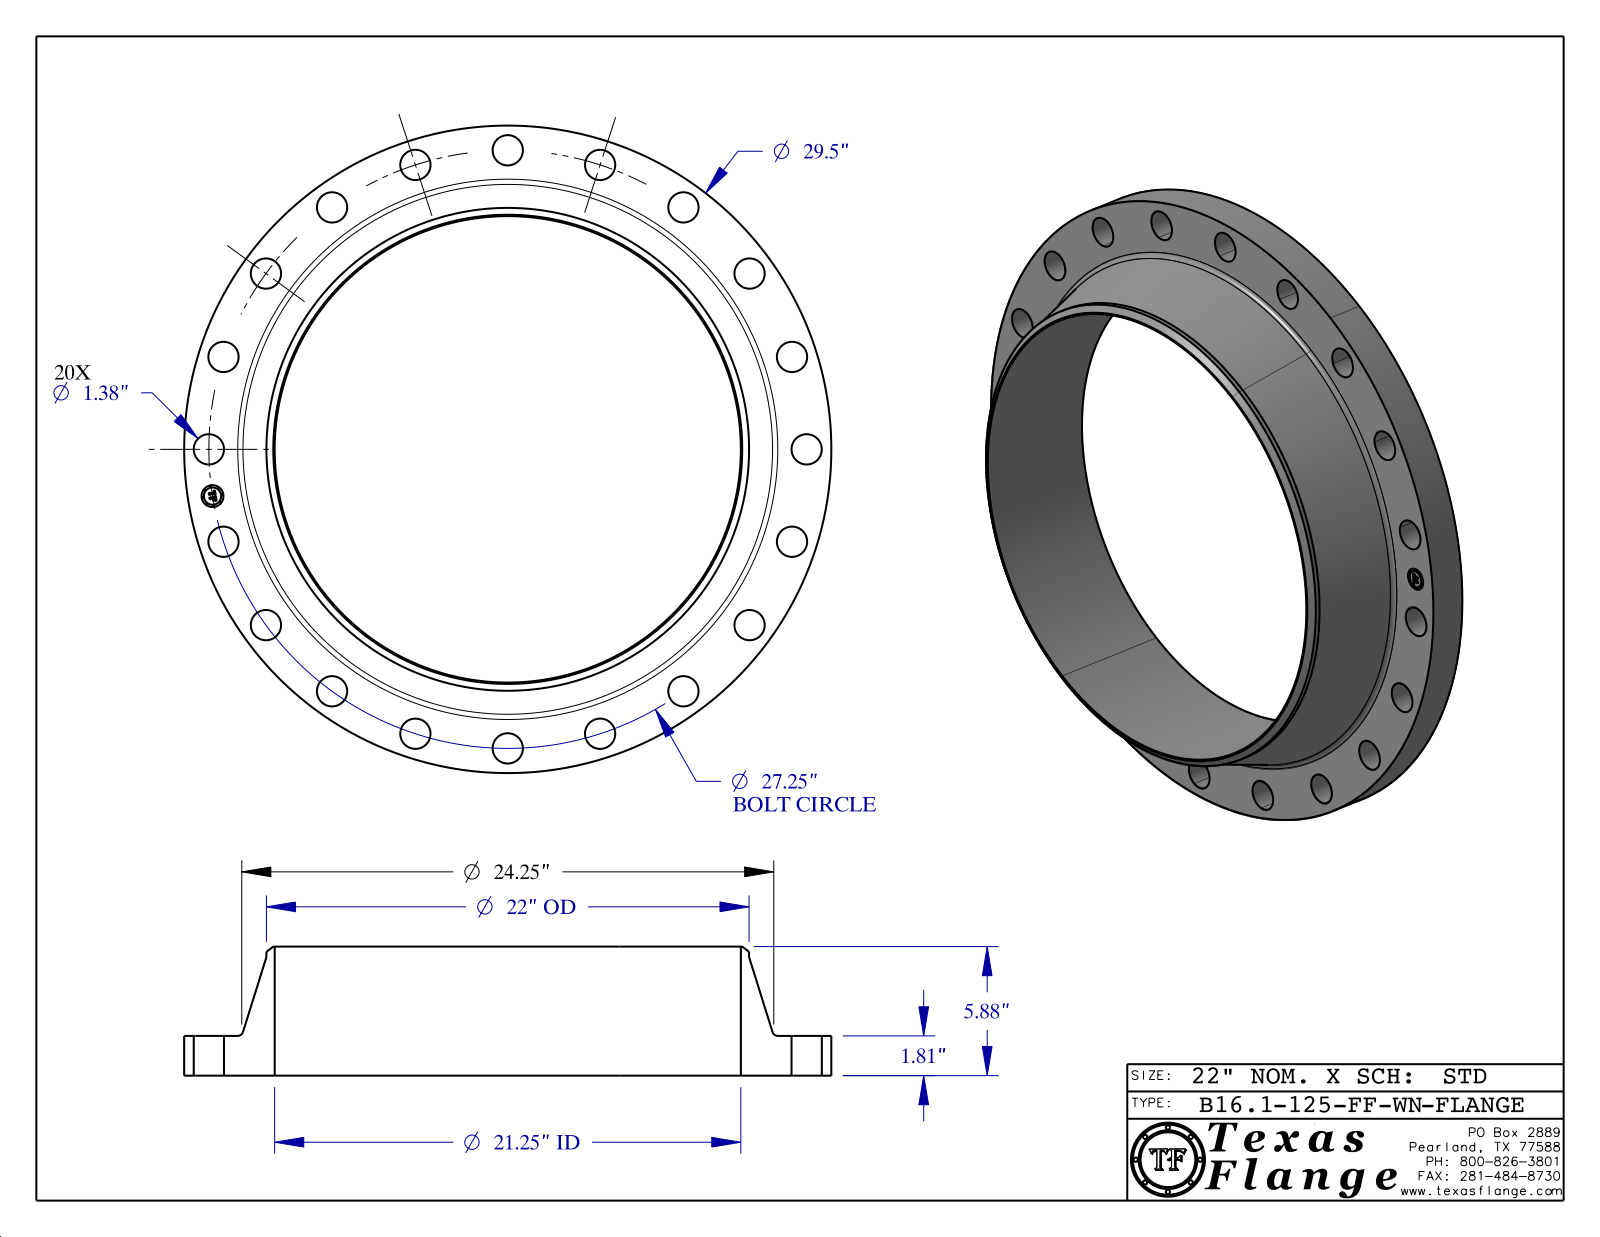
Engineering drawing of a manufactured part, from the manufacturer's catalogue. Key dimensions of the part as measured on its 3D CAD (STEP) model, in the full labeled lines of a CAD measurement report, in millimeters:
Part name (STEP PRODUCT): B16.1, Class 125-FF-WN
STEP written by: CATIA V5 STEP AP214 (AUTOMOTIVE_DESIGN)
Units: millimetres
Bodies: 1 solid, 440 faces (368 planar, 66 cylindrical, 6 other)
Overall size (bounding box): 749.3 × 749.3 × 149.4
Volume: 12 900 000 mm³ · Surface area: 983 900 mm²
Round holes (diameter × count): ⌀35.1 ×20, ⌀25.4 ×1, ⌀539.8 ×1
Round bosses / shafts (diameter × count): ⌀1.5 ×8, ⌀749.3 ×1, ⌀558.8 ×1, ⌀20 ×1
Main face-to-face distances: 46, 149.4, 103.4, 45.6, 0.4, 103.8, 7.6, 7.4, 1.4, 4.9
Hole centre spacings: 346.1, 489.4, 658.3, 213.9, 314.2, 108.3, 406.8, 560
